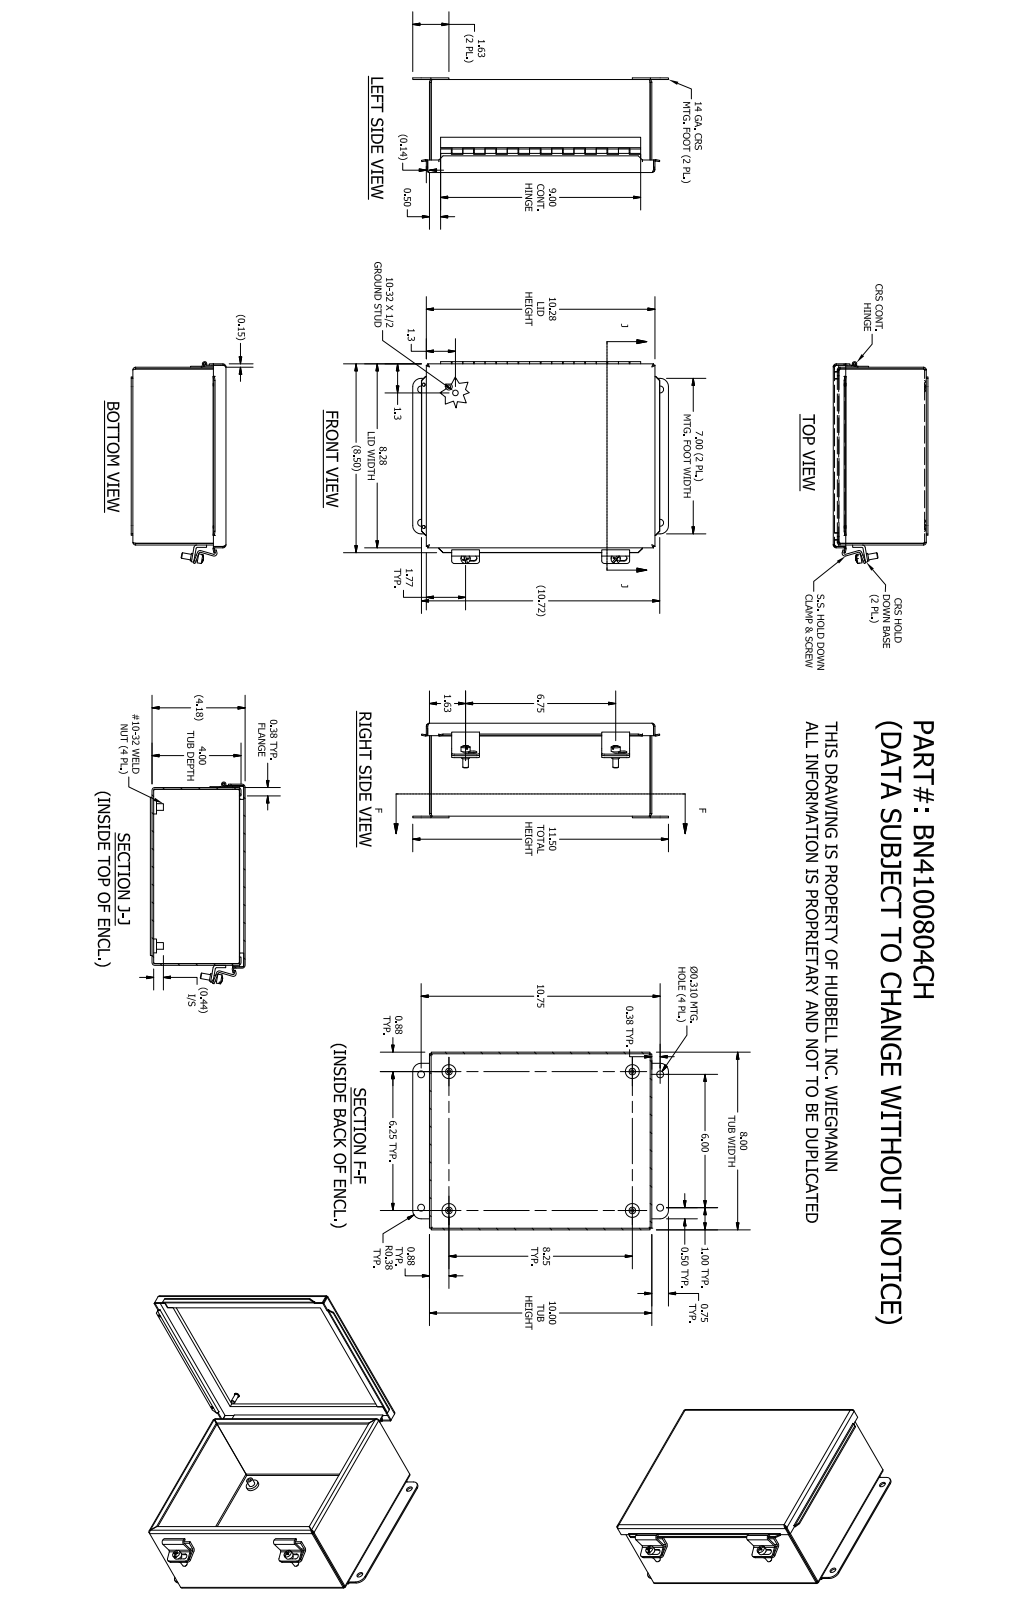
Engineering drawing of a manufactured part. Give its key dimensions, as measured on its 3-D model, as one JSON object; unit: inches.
{"part_name": "B_1008CH_LID; 316164; 38811; 3499 (+8 more)", "step_written_by": "Autodesk Inventor 2016 (AUTOMOTIVE_DESIGN)", "units": "inches", "bodies": {"solids": 20, "faces": 487, "planar": 313, "cylindrical": 123, "other": 51}, "overall_size": [11.5, 9.086, 4.259], "volume_in3": 30.54, "surface_area_in2": 841.8, "round_holes": [[0.156, 4], [0.31, 4], [0.14, 2], [0.196, 2], [0.117, 1]], "round_bosses_or_shafts": [[0.625, 4], [0.3, 4], [0.25, 3], [0.409, 2], [0.344, 2], [0.2, 1], [0.19, 1], [0.1, 1]], "partial_cylinders_radius": [[0.047, 8], [0.121, 8], [0.125, 8], [0.078, 4], [0.133, 4], [0.137, 4], [0.375, 4], [0.031, 3]], "face_to_face_distances": [0.074, 4.125, 0.059, 4.184, 4.051, 4.11, 7.926, 9.926, 8, 7.852], "hole_center_spacings": [1.256, 9.501, 6, 6.25, 6.251, 6.252, 8.25, 10.35]}
